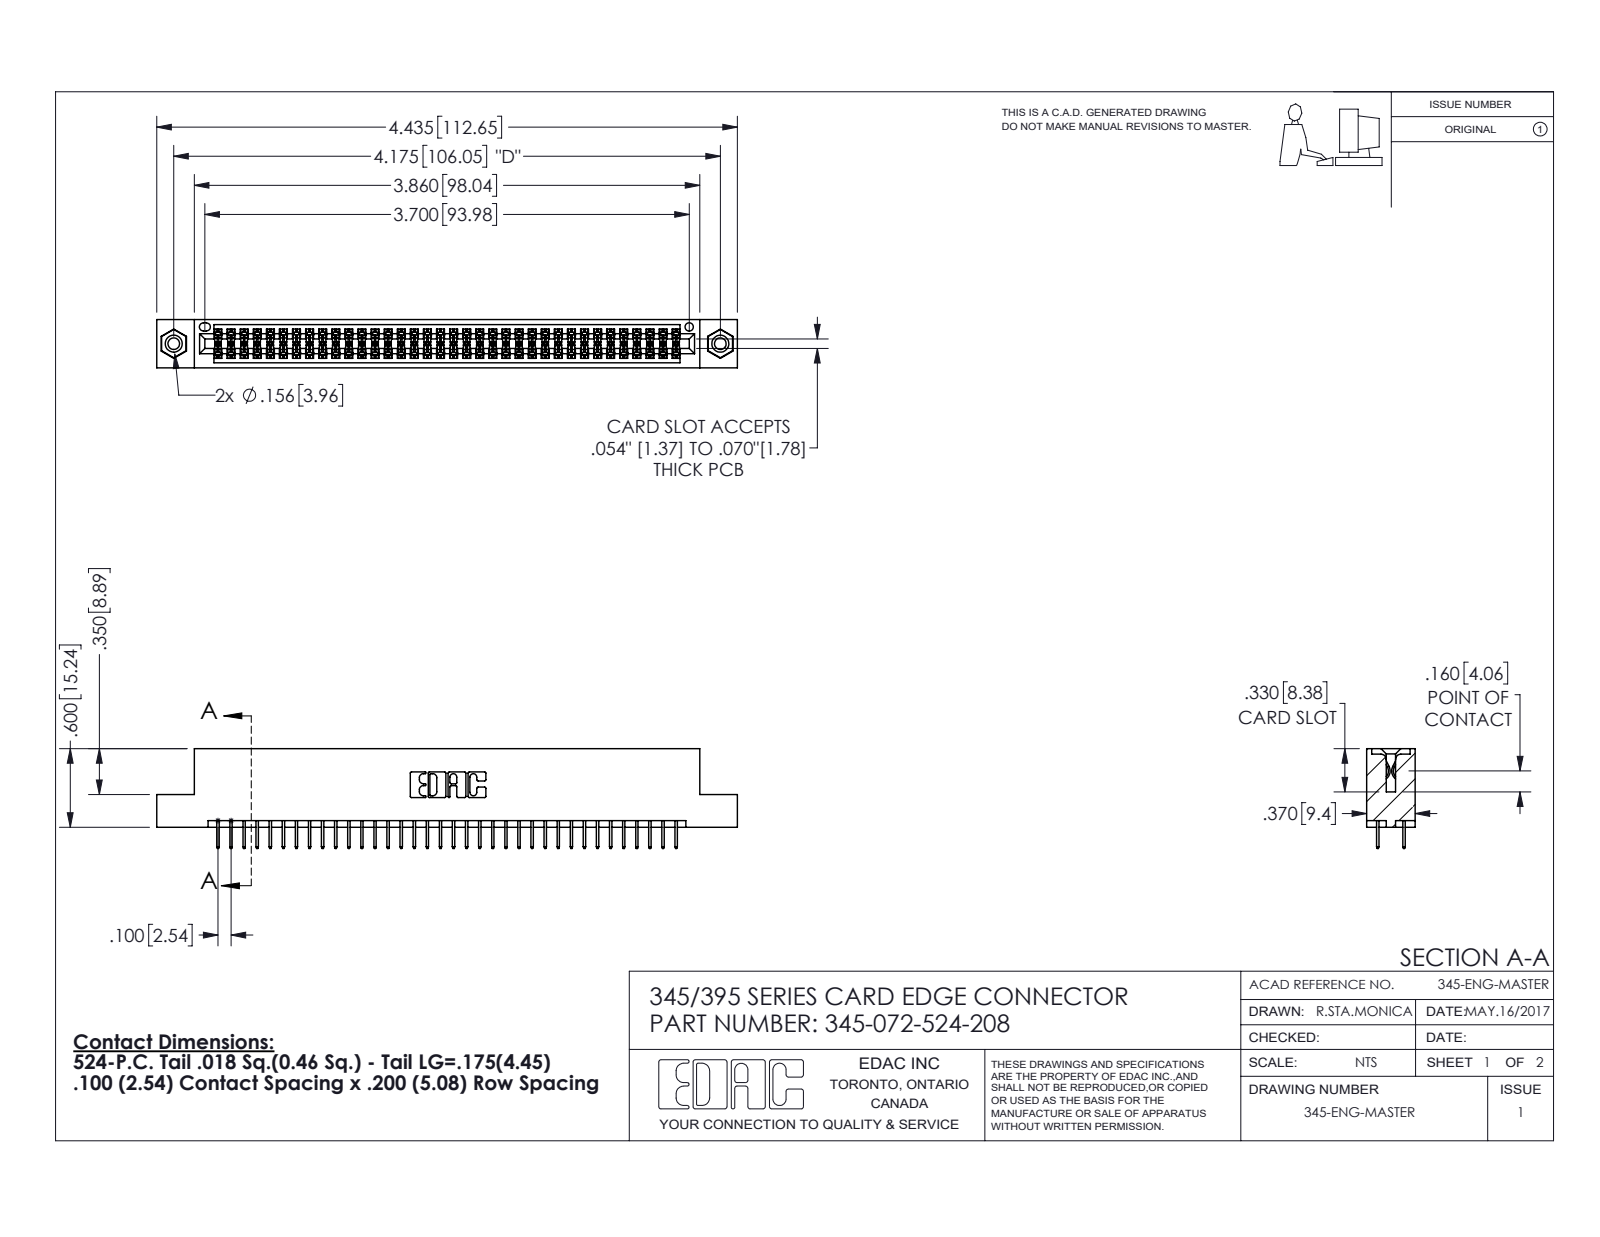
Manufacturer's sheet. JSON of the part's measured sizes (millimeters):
{"part_name": "345-292-001_345-293-124; 345 Part_Flush Mounting Lugs - 0.156 Dia-TI; 345-250-001_345-250-003-102; 345-072-524-208", "step_written_by": "SolidWorks 2016 (CONFIG_CONTROL_DESIGN)", "units": "millimeters", "bodies": {"solids": 75, "faces": 4074, "planar": 2920, "cylindrical": 1138, "other": 16}, "overall_size": [112.6, 19.4, 9.4], "volume_mm3": 10800, "surface_area_mm2": 15530, "round_holes": [[2.3, 2], [3.2, 2], [4, 2], [1.6, 1]], "round_bosses_or_shafts": [[3.9, 2]], "partial_cylinders_radius": [[0.2, 108], [0.3, 22], [0.2, 6], [0.8, 6], [0.7, 3], [0.4, 2], [0.5, 2], [0.6, 2]], "face_to_face_distances": [1.8, 7.6, 5.1, 9.4, 2.5, 6.9, 0.6, 5.7, 1.8, 4.4], "hole_center_spacings": [6.9, 100.1, 106]}
